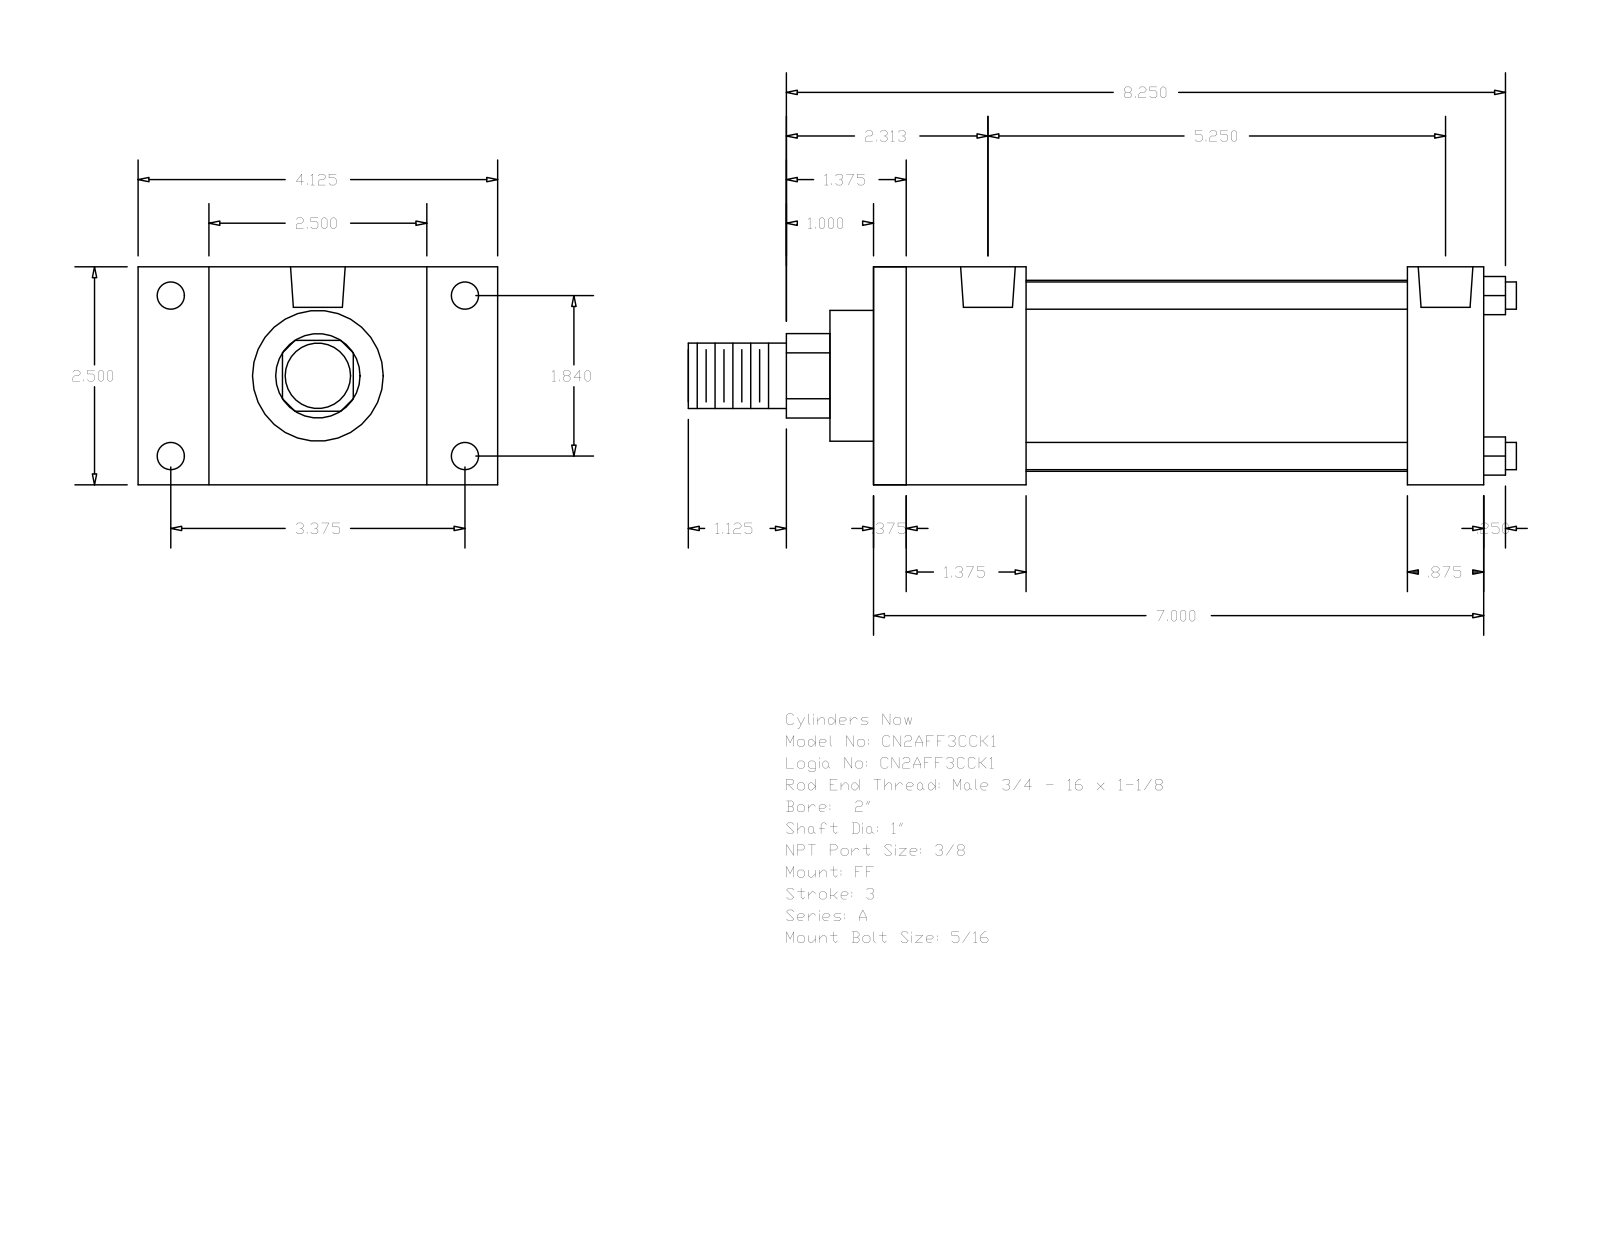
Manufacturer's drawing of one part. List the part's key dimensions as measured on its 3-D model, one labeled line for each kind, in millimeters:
Part name (STEP PRODUCT): A_FF__0200_1
STEP written by: GSSL Pune (CONFIG_CONTROL_DESIGN)
Units: millimetres
Bodies: 0 solids, 92 faces (64 planar, 28 cylindrical, 0 other)
Overall size (bounding box): 241.3 × 104.78 × 63.5
Round holes (diameter × count): ⌀5.56 ×4, ⌀7.94 ×4, ⌀15.93 ×2
Round bosses / shafts (diameter × count): ⌀7.94 ×4, ⌀55.63 ×1, ⌀38.1 ×1, ⌀25.4 ×1, ⌀19.05 ×1
Partial cylindrical surfaces — rounded edges, fillets, slot ends (radius × count): R12.29 ×1
Main face-to-face distances: 63.5, 177.8, 9.52, 168.28, 20.64, 44.45, 155.57, 34.93, 146.05, 111.12
Hole centre spacings: 46.74, 85.72, 97.63, 127.78, 1.59, 3.98, 129.37, 131.76
